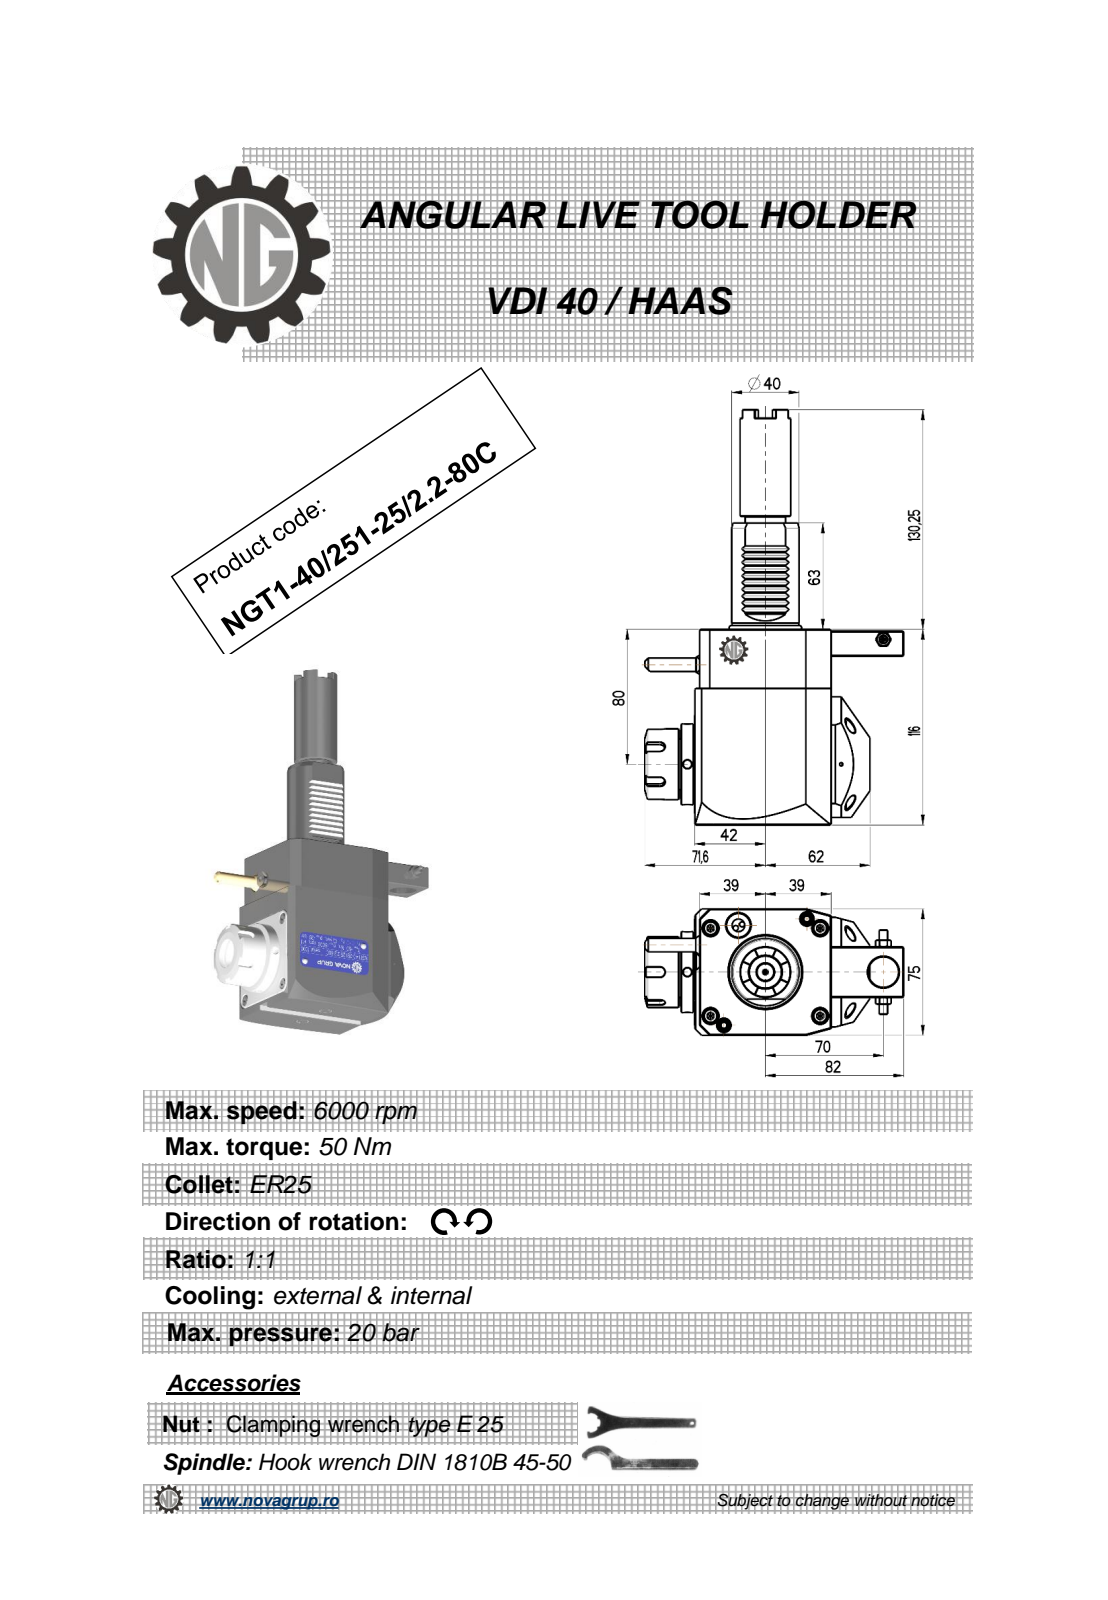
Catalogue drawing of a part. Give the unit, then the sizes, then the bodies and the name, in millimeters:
Units: millimetres
Overall size (bounding box): 246.25 × 153.6 × 76.6
Round holes (diameter × count): ⌀5 ×3, ⌀3 ×1, ⌀4.2 ×1, ⌀9.5 ×1, ⌀18 ×1, ⌀19.5 ×1, ⌀20.3 ×1
Round bosses / shafts (diameter × count): ⌀48 ×1, ⌀42 ×1, ⌀40 ×1, ⌀37.5 ×1, ⌀33 ×1, ⌀30 ×1, ⌀24 ×1, ⌀10 ×1
Partial cylindrical surfaces — rounded edges, fillets, slot ends (radius × count): R0.26 ×12, R0.3 ×10, R0.2 ×6, R3 ×5, R0.5 ×1, R40 ×1
Main face-to-face distances: 75, 116, 81, 3, 78, 2.8, 80.8, 1, 112, 11
Hole centre spacings: 20.93, 46.25, 61.13, 70, 72.5, 116.25, 137.8
Volume: 919 921 mm³ · Surface area: 79 011 mm²
Bodies: 1 solid, 482 faces (227 planar, 92 cylindrical, 163 other)
Part name (STEP PRODUCT): NGT1_40_251_25_2_2_80C
STEP written by: PRO/ENGINEER BY PARAMETRIC TECHNOLOGY CORPORATION, 2010280 (CONFIG_CONTROL_DESIGN)
